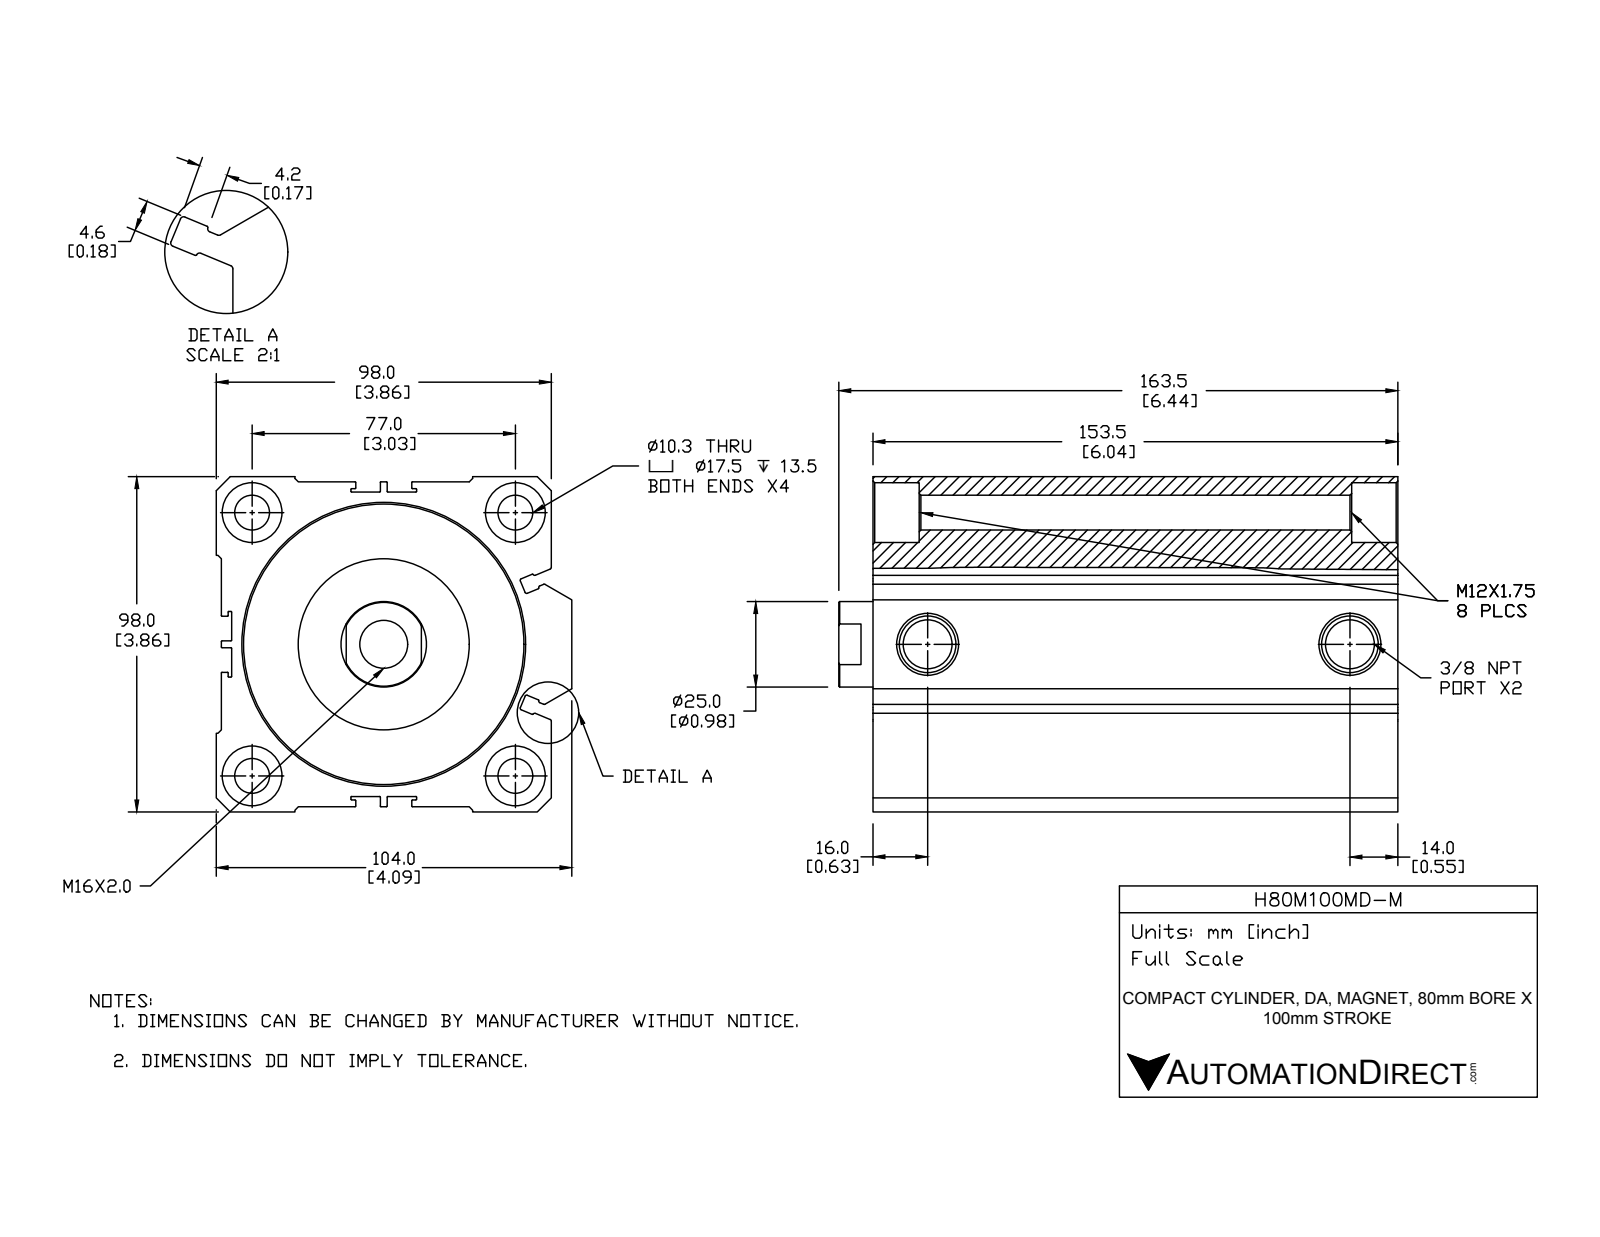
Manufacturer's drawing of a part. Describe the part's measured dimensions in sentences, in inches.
The part is named "H80M100MD-M; H80M100MD-M-PISTON; H80M100MD-M-BODY". Its 3-D file was written by "SolidWorks 2015 (CONFIG_CONTROL_DESIGN)". It is 2 solids with 261 faces: 105 planar, 103 cylindrical and 53 other. Overall it measures 6.437 by 4.094 by 3.858 inches. Its volume is 53.13 cubic inches and its surface area 291.1 square inches. Round holes: 4 of diameter 0.402, 4 of diameter 0.689, 2 of diameter 0.562, 1 of diameter 0.551, 1 of diameter 0.984, 1 of diameter 1.792, 1 of diameter 3.15, 1 of diameter 3.228. Round bosses or shafts: 1 of diameter 1.969, 1 of diameter 1.535. Partial cylindrical surfaces (rounded edges, fillets, slot ends): 40 of radius 0.008, 12 of radius 0.02. The main face-to-face distances are 0.059, 3.799, 3.858, 0.177, 0.118, 3.681, 3.74, 3.622, 0.079, 0.354. The hole center spacings are 2.144, 3.031, 4.287, 4.862.
